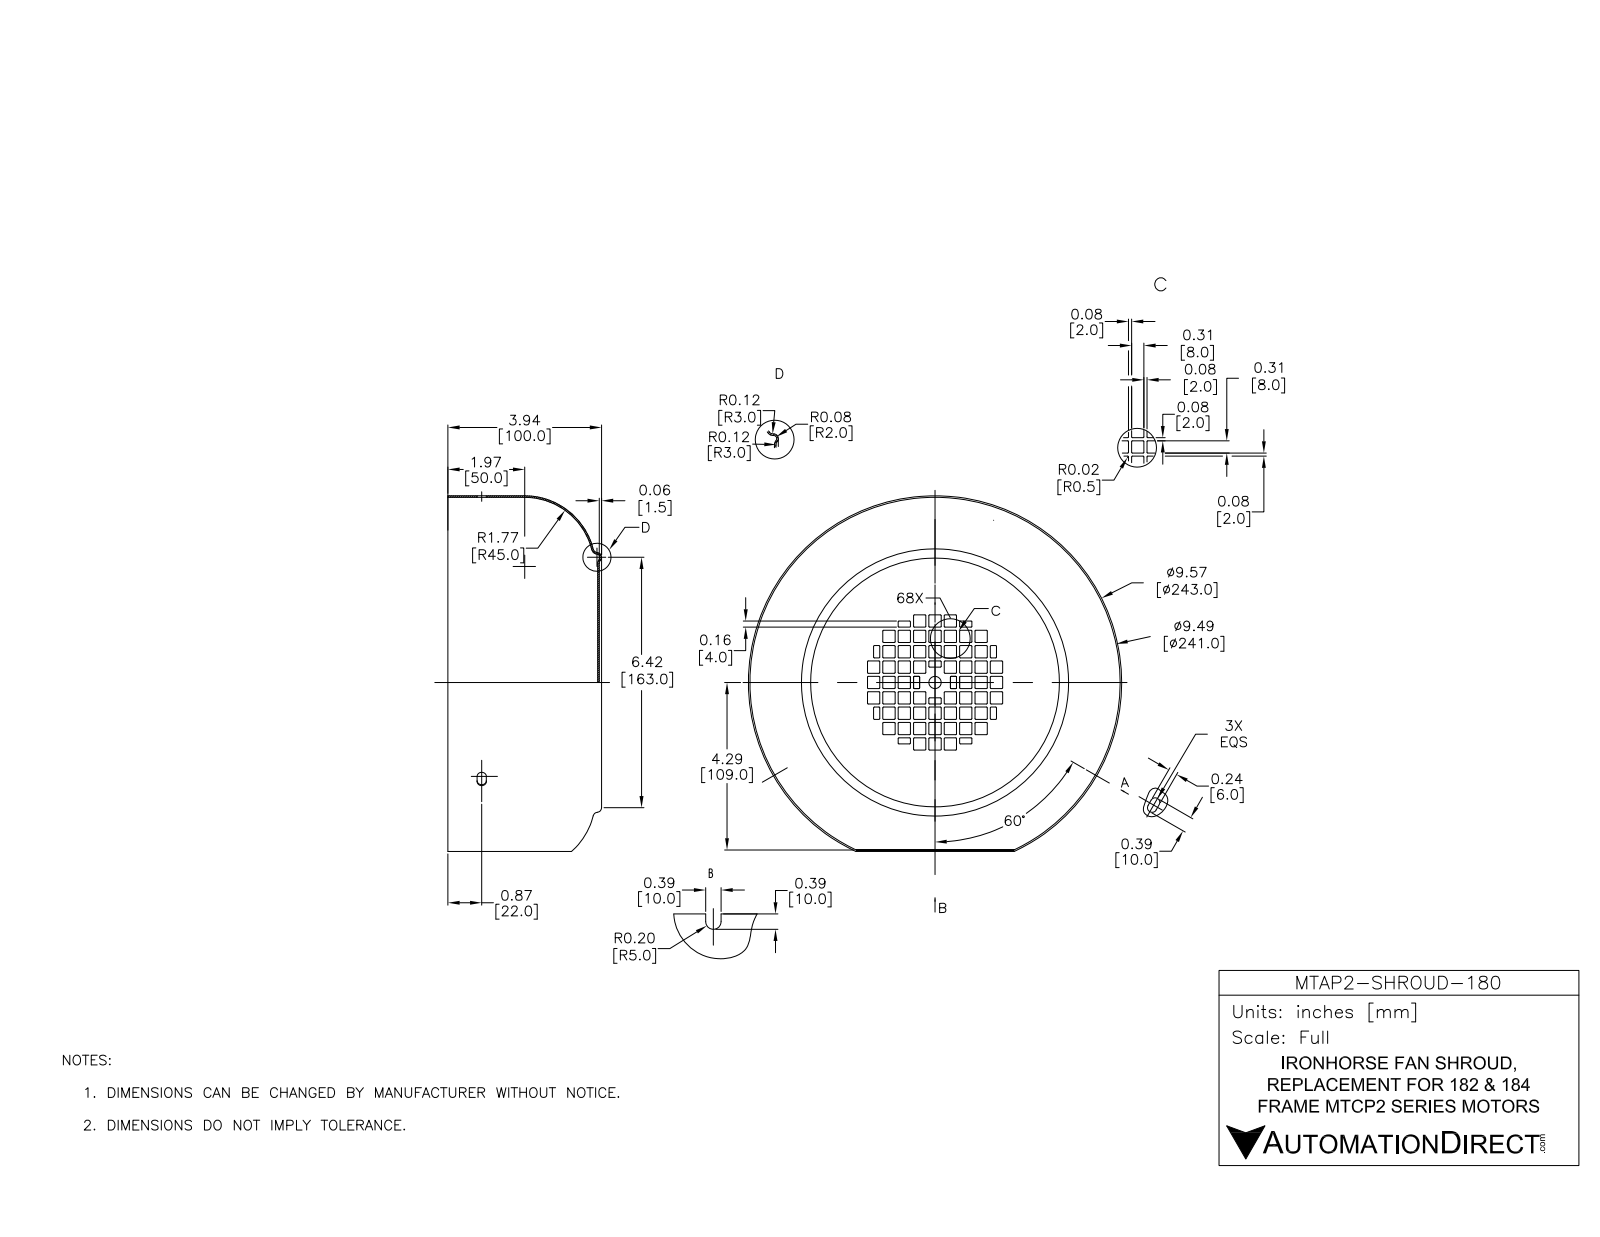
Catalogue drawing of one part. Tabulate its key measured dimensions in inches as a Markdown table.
| quantity | value |
| --- | --- |
| part name | MTAP2-SHROUD-180 |
| STEP written by | SolidWorks 2017 (AUTOMOTIVE_DESIGN) |
| units | inches |
| bodies | 2 solids, 624 faces (335 planar, 266 cylindrical, 23 other) |
| overall size | 9.567 × 9.252 × 3.937 |
| volume | 6.242 in³ |
| surface area | 325.7 in² |
| round holes (diameter × count) | 0.315 × 1, 9.488 × 1 |
| round bosses / shafts (diameter × count) | 9.567 × 1, 0.394 × 1 |
| partial cylindrical surfaces (radius × count) | 0.02 × 256 |
| main face-to-face distances | 0.039, 0.02, 3.858, 3.839, 3.878, 0.394, 0.787, 1.181, 0.315, 1.575 |
